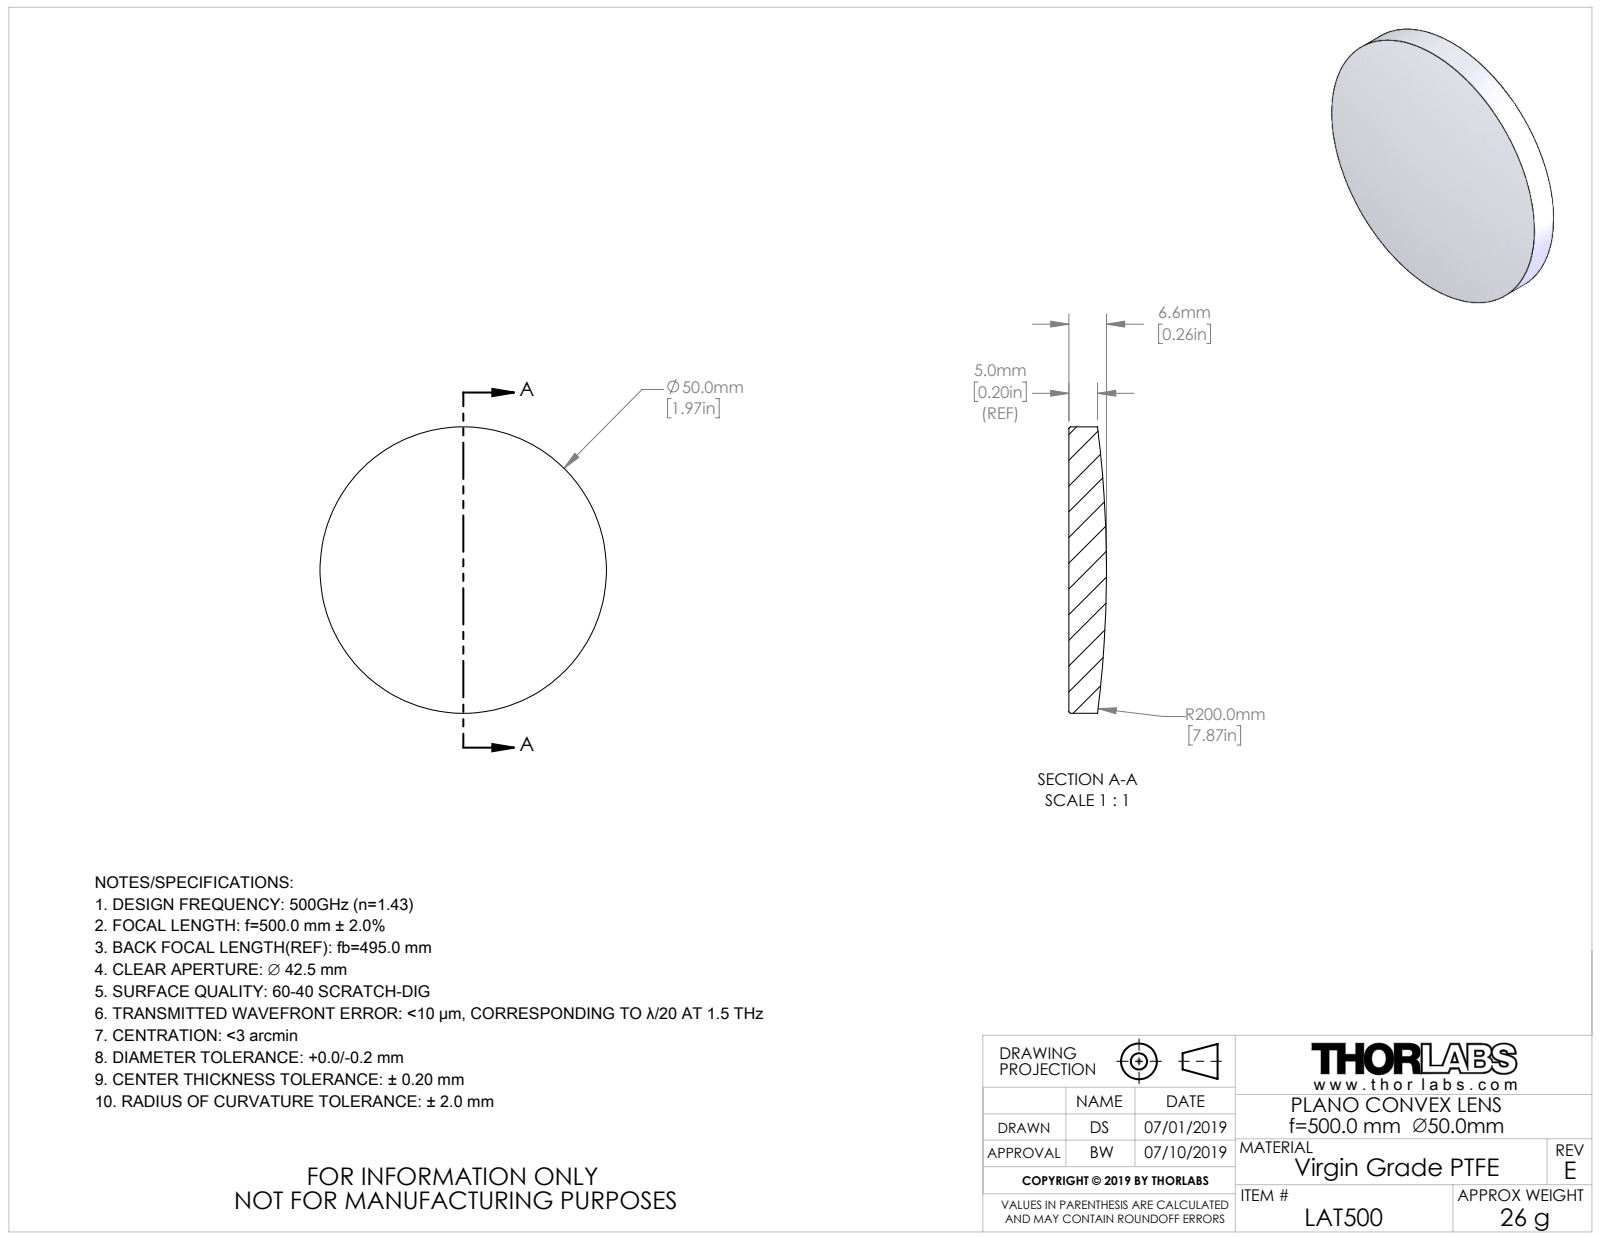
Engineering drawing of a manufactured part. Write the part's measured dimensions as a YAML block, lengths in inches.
part_name: "12649-E0W"
step_written_by: "SolidWorks 2018 (CONFIG_CONTROL_DESIGN)"
units: inches
bodies: {solids: 1, faces: 7, planar: 1, cylindrical: 2, other: 4}
overall_size: [1.969, 1.969, 0.259]
volume: 0.693
surface_area: 7.28
round_bosses_or_shafts:
  - {diameter: 1.969, count: 1}
